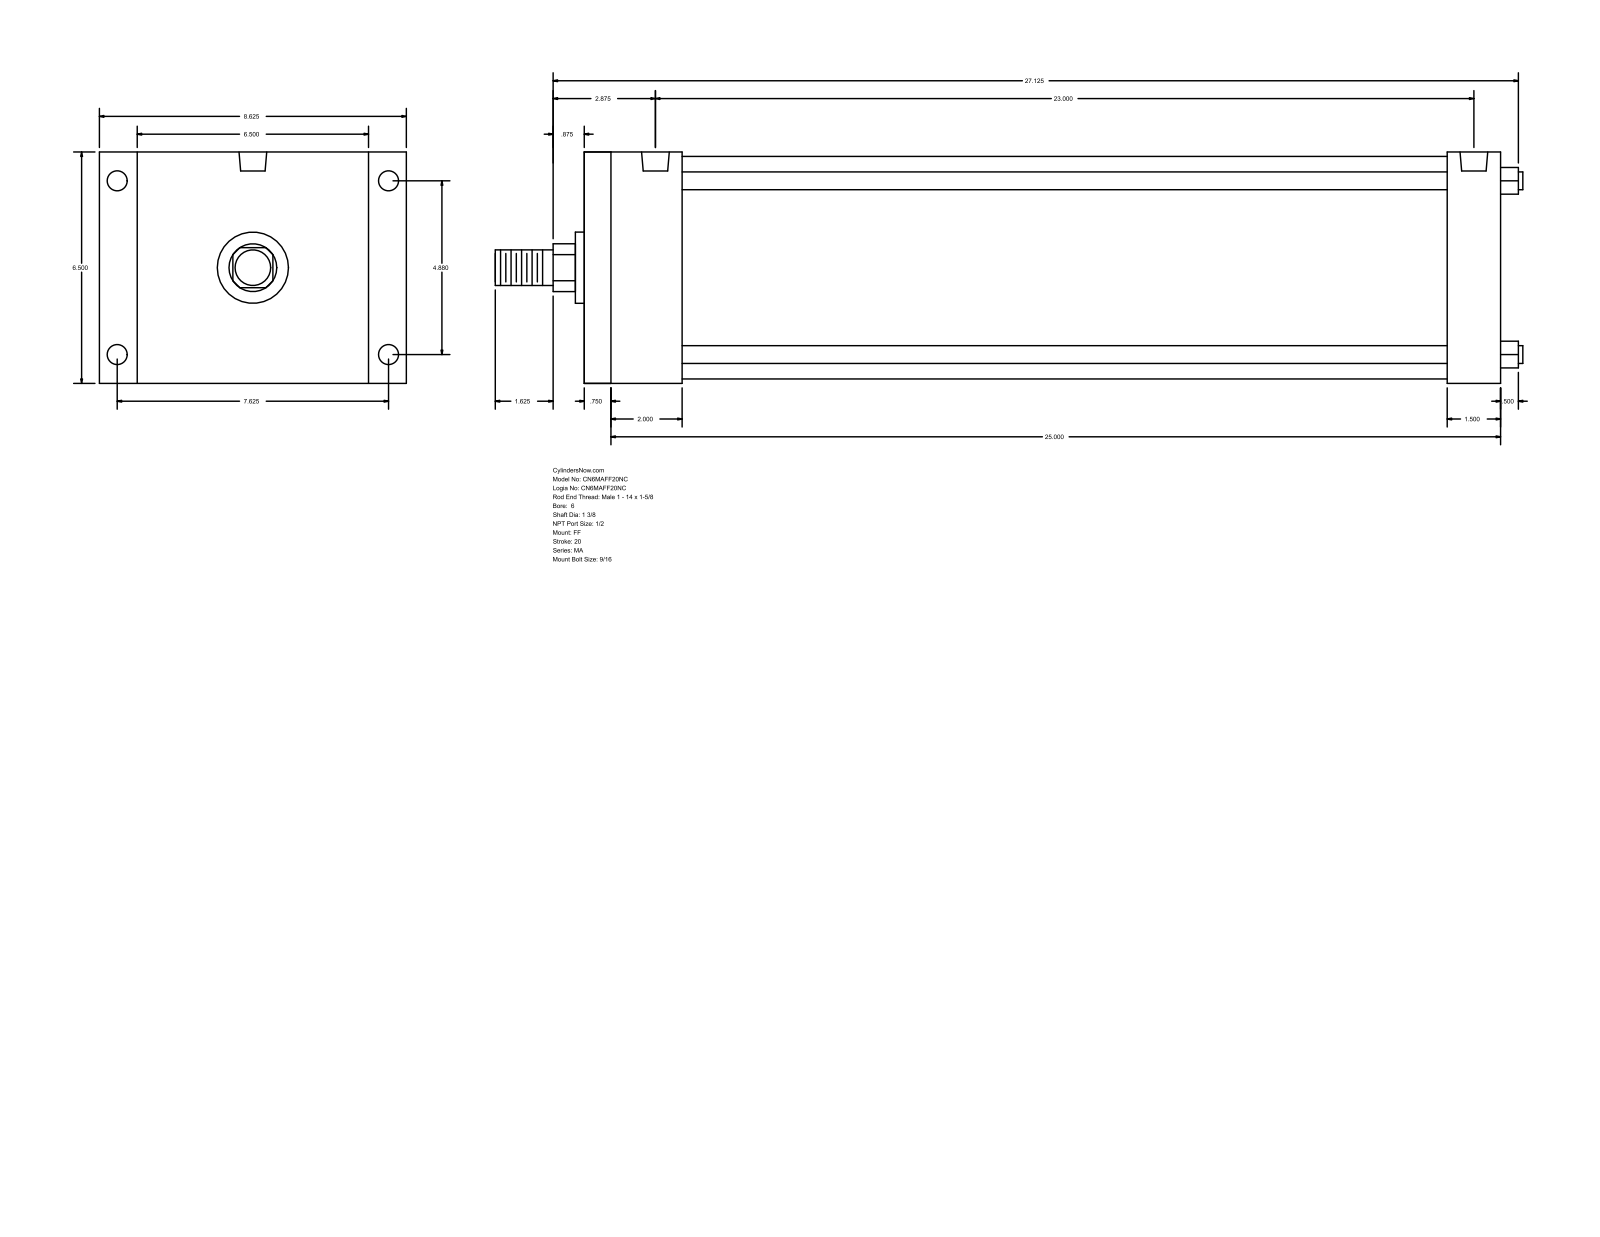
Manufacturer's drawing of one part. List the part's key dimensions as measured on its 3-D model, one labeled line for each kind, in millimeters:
Part name (STEP PRODUCT): MA_FF__0600_1.375
STEP written by: GSSL Pune (CONFIG_CONTROL_DESIGN)
Units: millimetres
Bodies: 0 solids, 92 faces (64 planar, 28 cylindrical, 0 other)
Overall size (bounding box): 733.42 × 219.07 × 165.1
Round holes (diameter × count): ⌀14.29 ×4, ⌀17.46 ×4, ⌀19.77 ×2
Round bosses / shafts (diameter × count): ⌀12.7 ×4, ⌀158.75 ×1, ⌀50.8 ×1, ⌀34.92 ×1, ⌀25.4 ×1
Partial cylindrical surfaces — rounded edges, fillets, slot ends (radius × count): R17.06 ×1
Main face-to-face distances: 165.1, 654.04, 638.17, 15.87, 38.1, 66.67, 50.8, 587.37, 615.94, 600.07
Hole centre spacings: 123.96, 193.68, 229.95, 587.38, 3.18, 584.2
